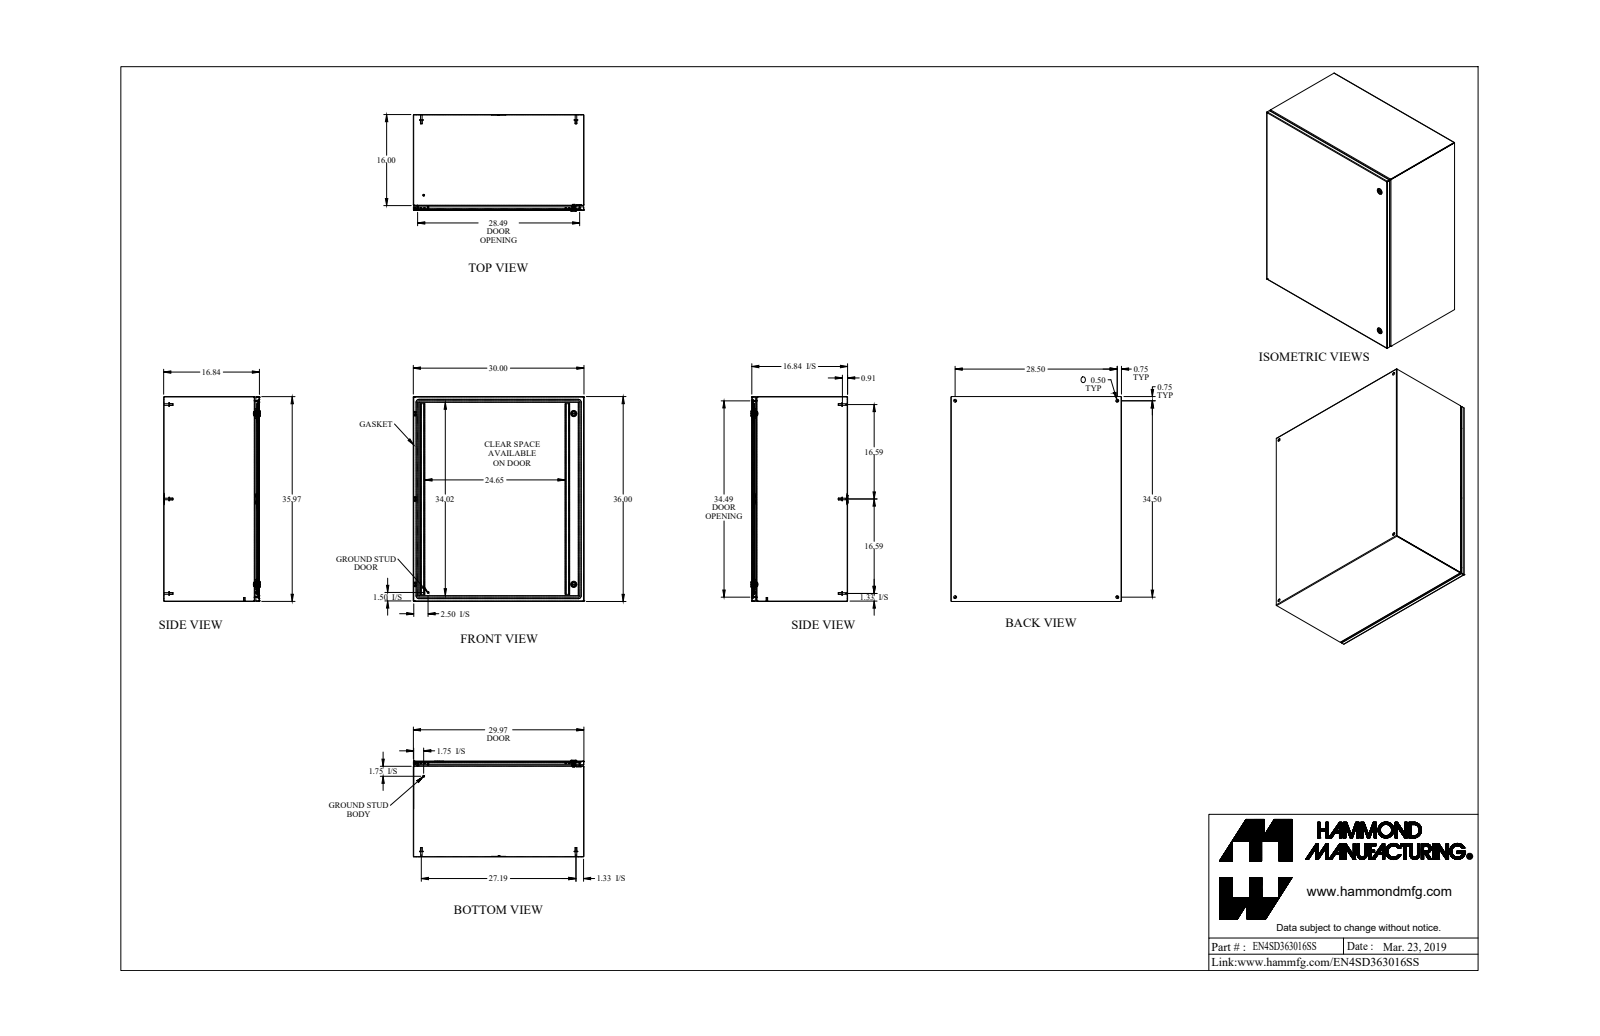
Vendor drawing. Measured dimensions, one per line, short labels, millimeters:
name: EN4SD363016SS
written by: SolidWorks 2019 (AUTOMOTIVE_DESIGN)
unit: mm
bodies: 37 solids, 943 faces (454 planar, 309 cylindrical, 180 other)
size: 914.4 × 762 × 431.9
volume: 5 622 000 mm³; area: 6 206 000 mm²
holes: 6× ⌀12.7, 2× ⌀5, 2× ⌀9.8, 2× ⌀16, 2× ⌀19.5, 1× ⌀4.4, 1× ⌀6.1, 1× ⌀6.1
bosses: 8× ⌀8, 6× ⌀7, 4× ⌀15.9, 4× ⌀15.9, 2× ⌀27.9, 2× ⌀19.9, 2× ⌀13.3, 2× ⌀6.4
rounds: 18× R0.9, 18× R2.7, 12× R0.3, 12× R1.2, 12× R7.9, 6× R0.2, 6× R1.6, 4× R3.2
face distances: 1.8, 426, 760.2, 424.1, 427.8, 912.6, 758.3, 762, 910.7, 914.4
hole spacings: 699.3, 723.9, 876.3, 1136.6, 63.2, 63.2, 762, 819.6
